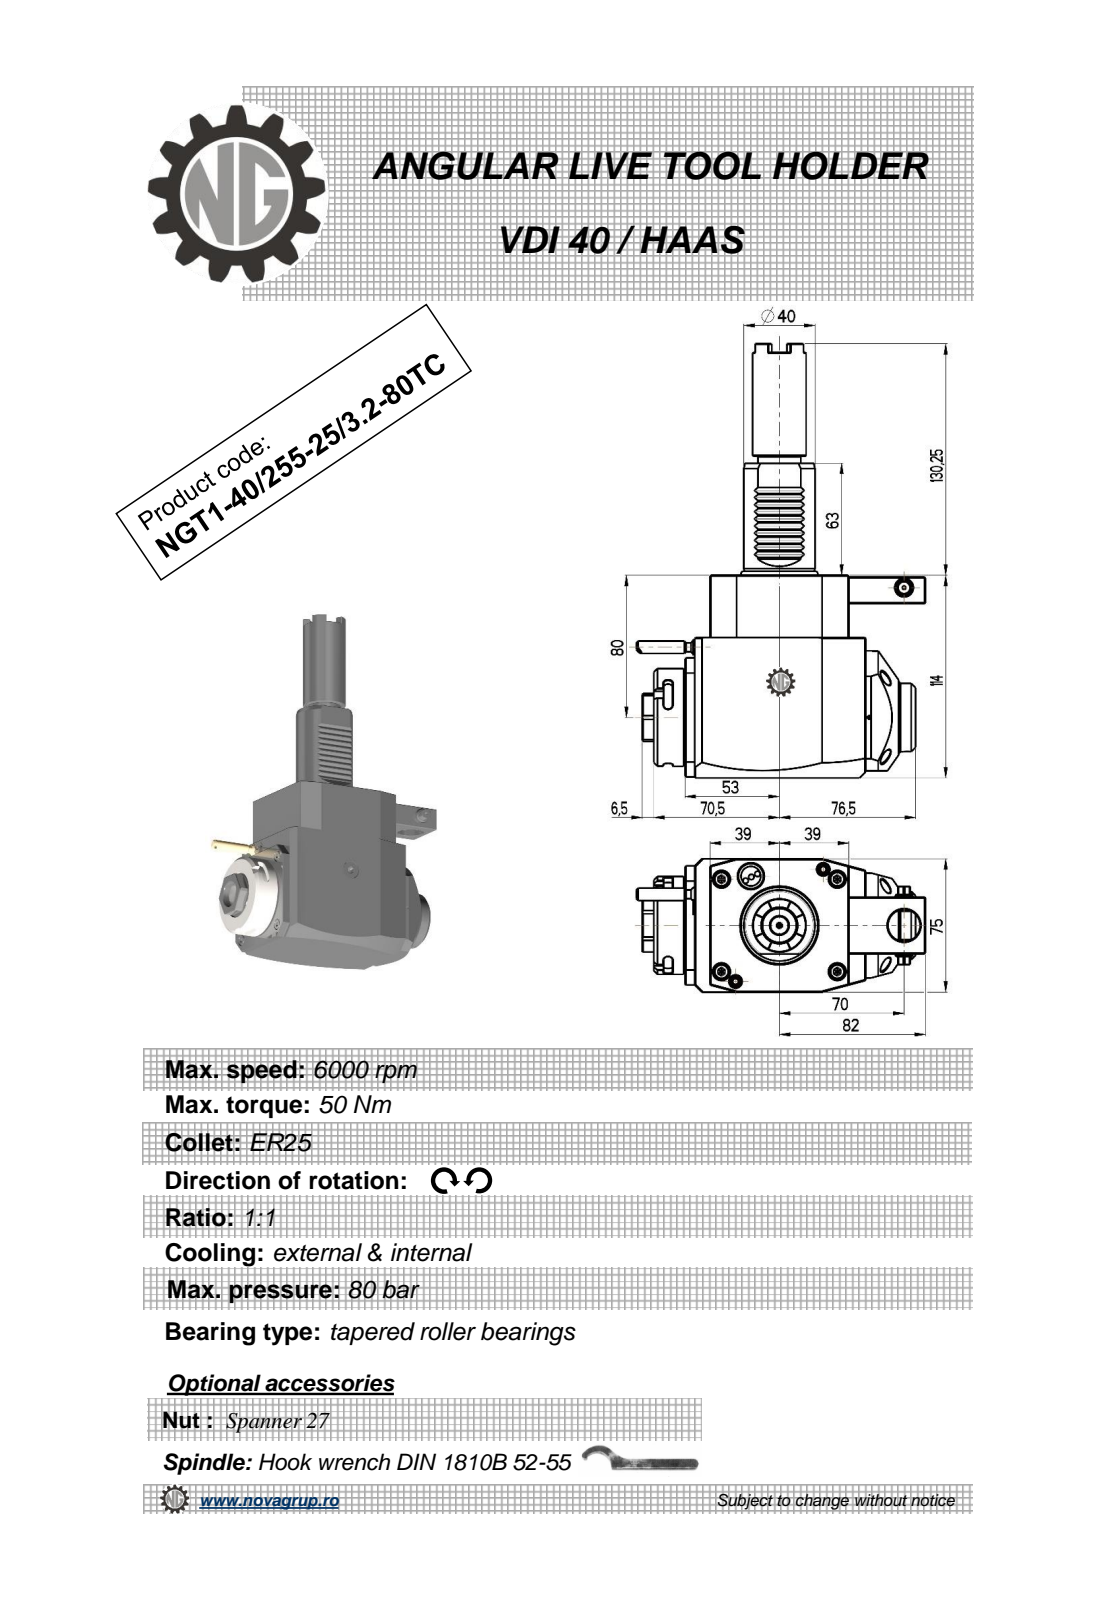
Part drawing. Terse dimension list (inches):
name: NGT1_40_255_25_3_2_80TC
written by: PRO/ENGINEER BY PARAMETRIC TECHNOLOGY CORPORATION, 2010280 (CONFIG_CONTROL_DESIGN)
unit: in
bodies: 1 solid, 391 faces (213 planar, 88 cylindrical, 90 other)
size: 9.616 × 6.391 × 2.953
volume: 61.88 in³; area: 125.1 in²
holes: 2× ⌀0.709, 1× ⌀0.079, 1× ⌀0.098, 1× ⌀0.118, 1× ⌀0.374, 1× ⌀0.787
bosses: 2× ⌀0.353, 1× ⌀2.165, 1× ⌀1.89, 1× ⌀1.575, 1× ⌀1.516, 1× ⌀1.181, 1× ⌀0.945, 1× ⌀0.394
rounds: 10× R0.012, 6× R0.098, 2× R7.087, 1× R0.02, 1× R0.152, 1× R0.167, 1× R0.591, 1× R0.965
face distances: 2.953, 4.488, 0.551, 0.689, 4.311, 3.11, 3.622, 3.071, 1.24, 3.858
hole spacings: 1.47, 1.701, 2.756, 2.854
